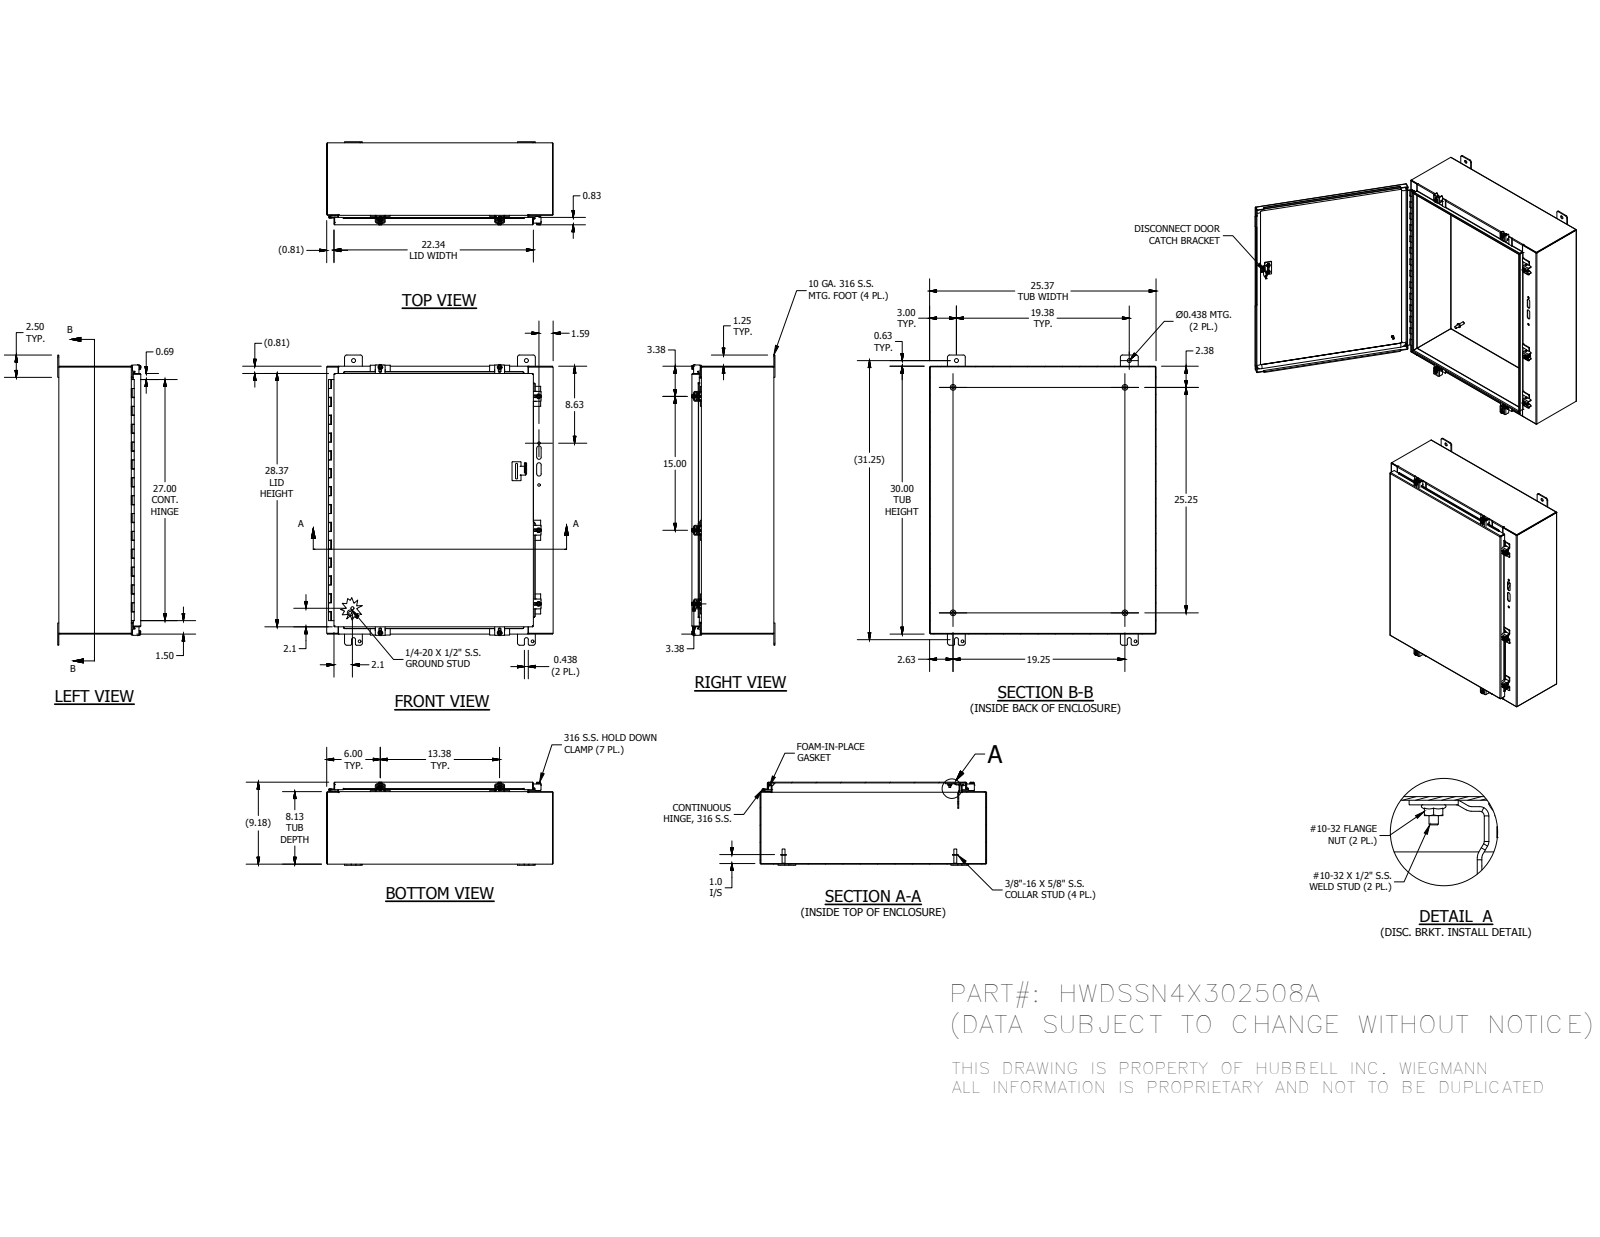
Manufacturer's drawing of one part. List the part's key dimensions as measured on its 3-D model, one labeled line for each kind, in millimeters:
Part name (STEP PRODUCT): SSN4X302508ABKP; 38859; 34839; 32874-30T (+8 more)
STEP written by: Autodesk Inventor 2016 (AUTOMOTIVE_DESIGN)
Units: millimetres
Bodies: 20 solids, 808 faces (481 planar, 245 cylindrical, 82 other)
Overall size (bounding box): 825.5 × 644.52 × 236.25
Volume: 3 562 000 mm³ · Surface area: 3 625 000 mm²
Round holes (diameter × count): ⌀7.95 ×4, ⌀11.13 ×4, ⌀3.96 ×2, ⌀7.14 ×2, ⌀3.17 ×1
Round bosses / shafts (diameter × count): ⌀15.88 ×4, ⌀8.38 ×4, ⌀8.56 ×3, ⌀6.35 ×2, ⌀4.83 ×2, ⌀3.05 ×1
Partial cylindrical surfaces — rounded edges, fillets, slot ends (radius × count): R0.79 ×27, R2.67 ×23, R6.35 ×21, R3.17 ×11, R0.25 ×8, R1.92 ×8, R2.38 ×5, R4.76 ×5
Main face-to-face distances: 1.88, 231.19, 229.31, 233.07, 760.12, 1.87, 204.5, 26.69, 644.52, 642.64
Hole centre spacings: 762, 907.1, 40.44, 476.08, 492.12, 492.13, 725.72, 28.58
